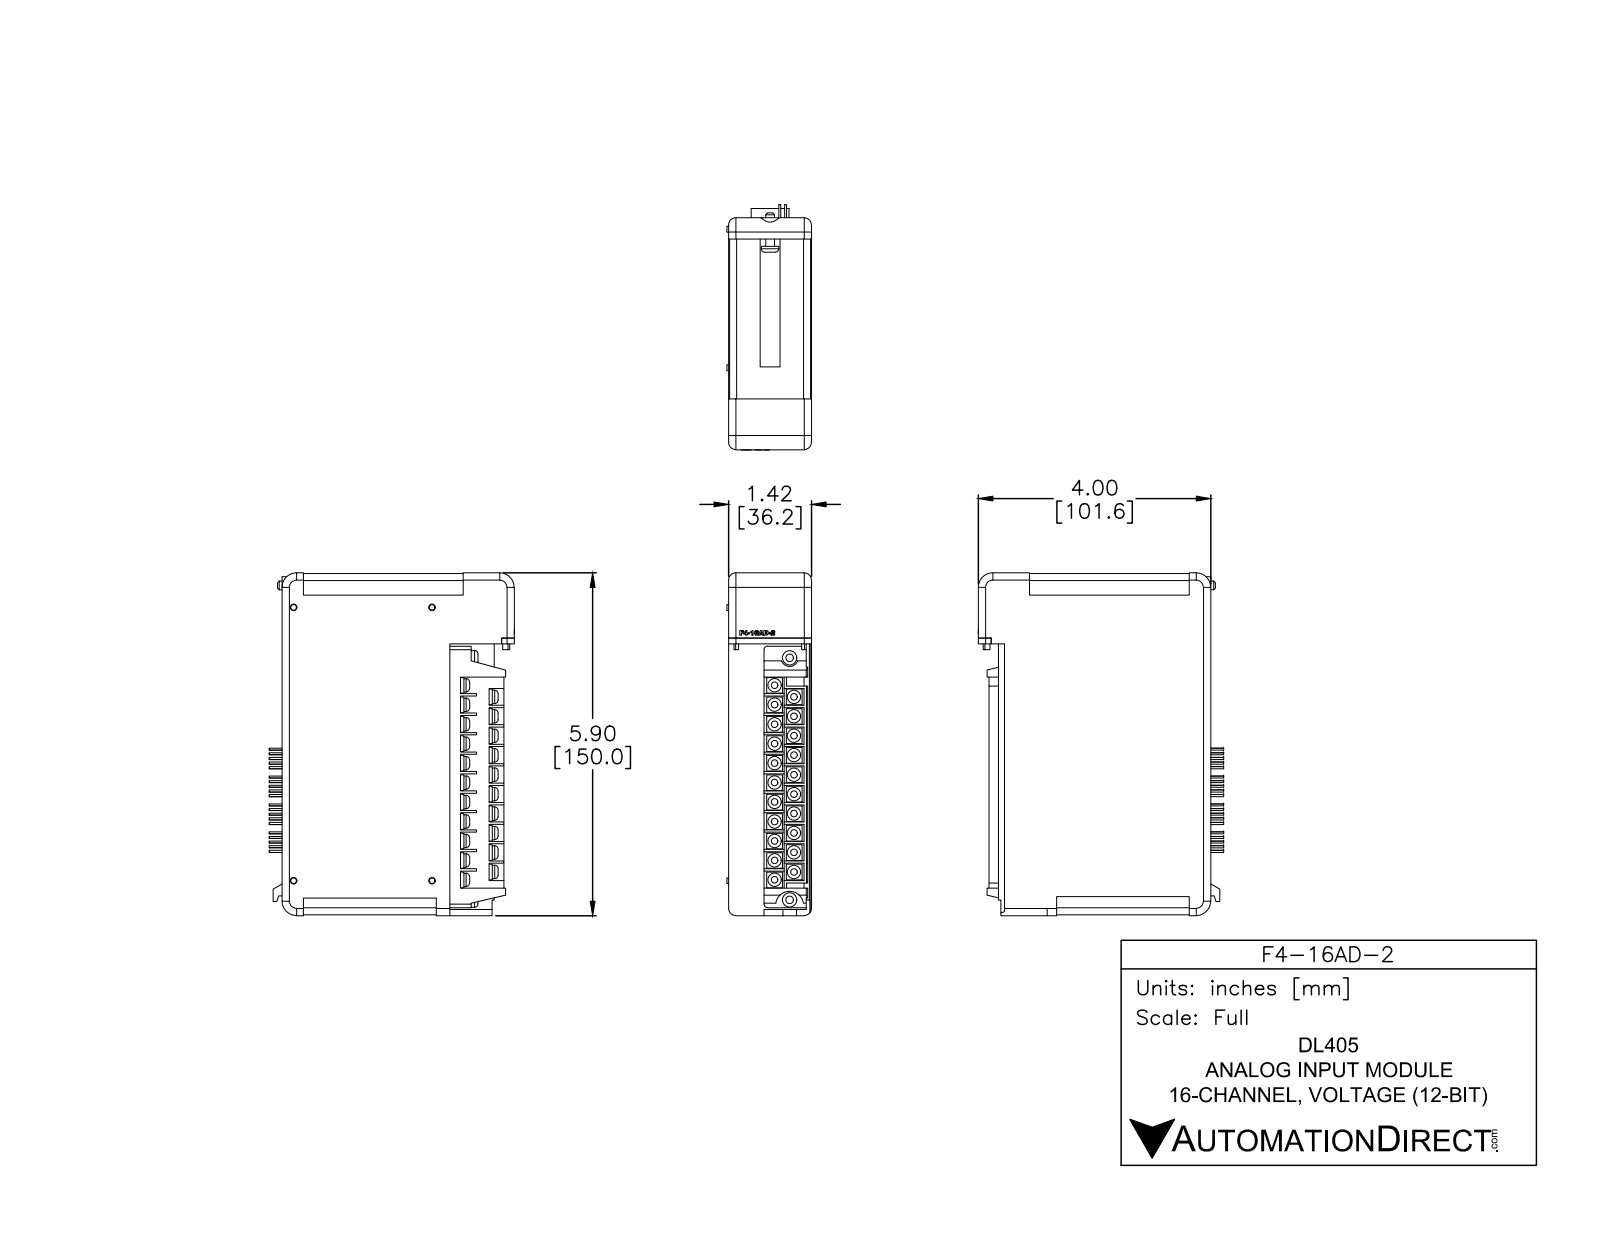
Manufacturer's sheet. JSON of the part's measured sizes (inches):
{"part_name": "F4-16AD-2", "step_written_by": "SolidWorks 2014 (AUTOMOTIVE_DESIGN)", "units": "inches", "bodies": {"solids": 6, "faces": 901, "planar": 560, "cylindrical": 246, "other": 95}, "overall_size": [5.905, 4.223, 1.455], "volume_in3": 27.6, "surface_area_in2": 90.48, "round_bosses_or_shafts": [[0.23, 21], [0.035, 20], [0.035, 20], [0.25, 2], [0.3, 1], [0.15, 1]], "partial_cylinders_radius": [[0.015, 82], [0.125, 8], [0.12, 4], [0.25, 3], [0.03, 2], [0.06, 2], [0.149, 1], [0.151, 1]], "face_to_face_distances": [1.425, 0.015, 2.89, 5.875, 1.41, 0.47, 0.955, 5.89, 1.21, 0.345]}
